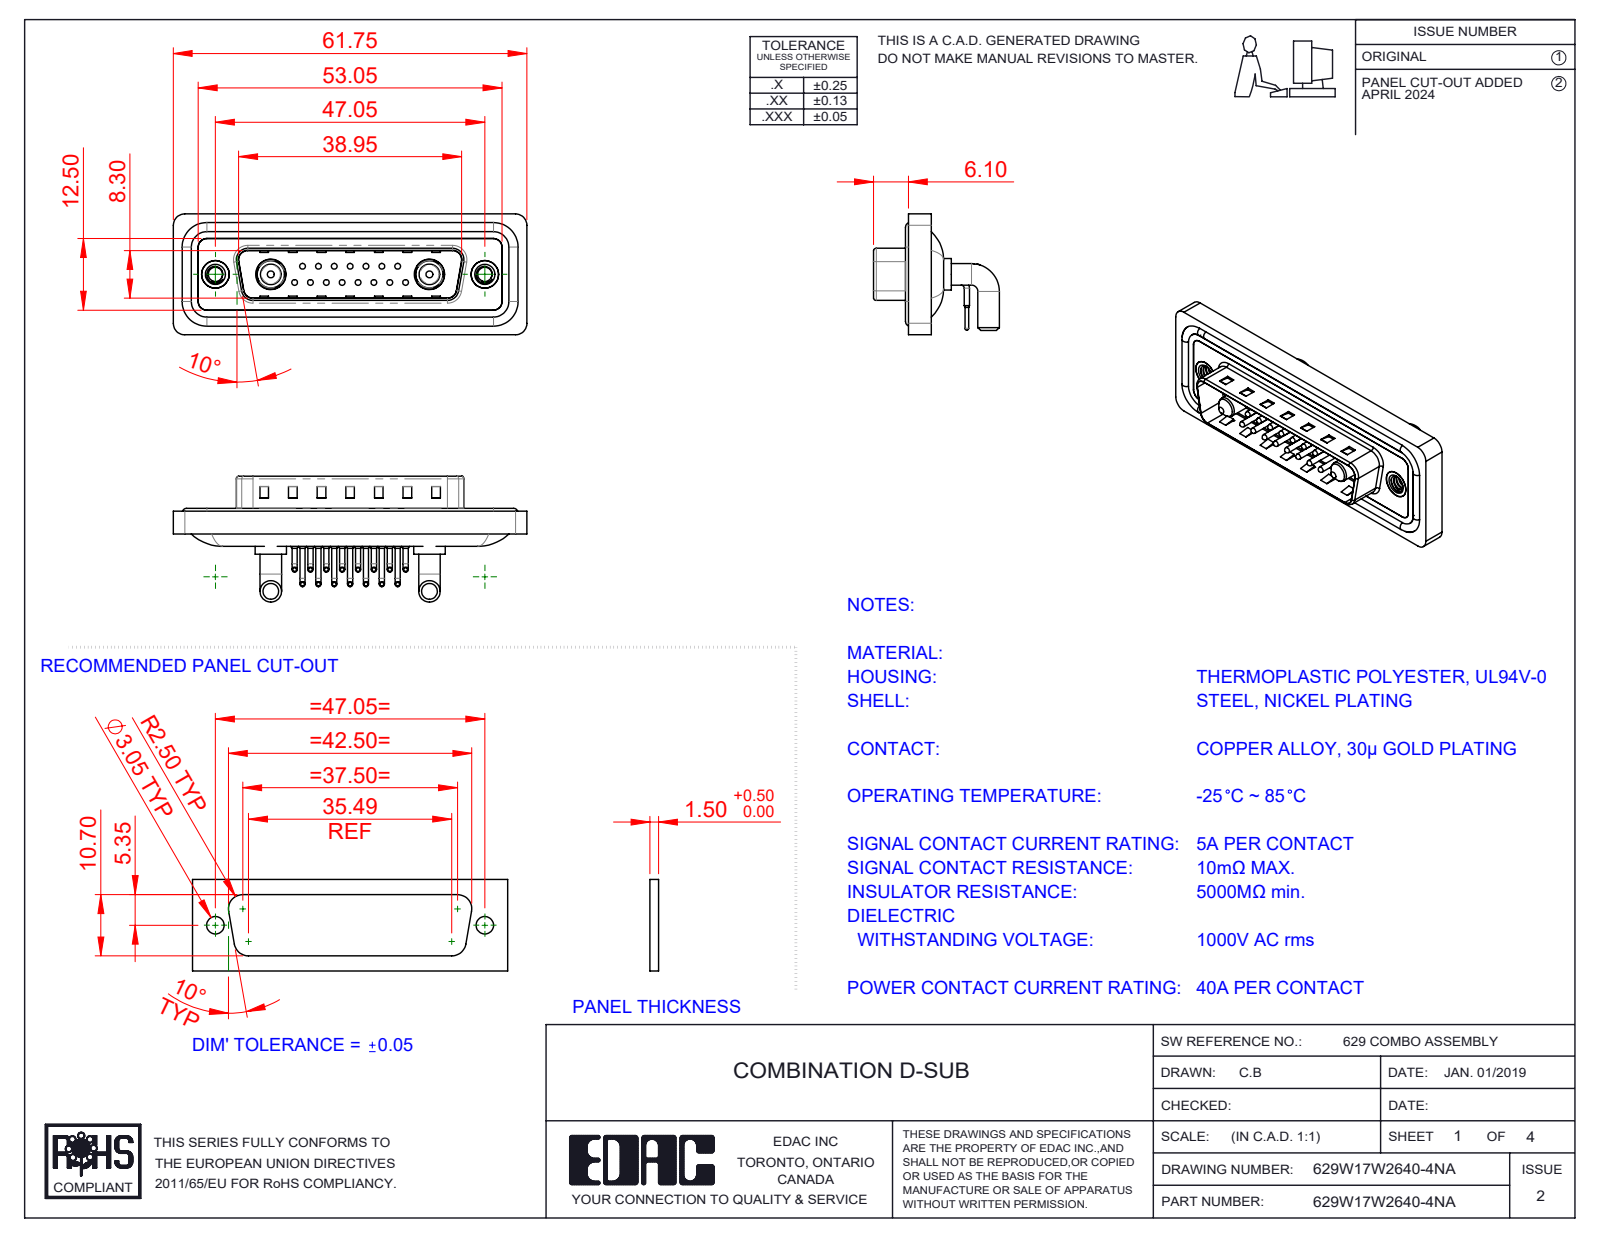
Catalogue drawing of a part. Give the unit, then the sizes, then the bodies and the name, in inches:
Units: inches
Overall size (bounding box): 2.431 × 0.865 × 0.831
Round holes (diameter × count): ⌀0.03 ×15, ⌀0.063 ×15, ⌀0.079 ×15, ⌀0.098 ×2, ⌀0.157 ×2, ⌀0.189 ×2, ⌀0.191 ×2, ⌀0.197 ×2, ⌀0.209 ×2
Round bosses / shafts (diameter × count): ⌀0.035 ×30, ⌀0.059 ×15, ⌀0.039 ×15, ⌀0.026 ×15, ⌀0.148 ×4, ⌀0.063 ×4, ⌀0.217 ×2, ⌀0.205 ×2
Partial cylindrical surfaces — rounded edges, fillets, slot ends (radius × count): R0.059 ×18, R0.079 ×18, R0.04 ×15, R0.02 ×8, R0.063 ×8, R0.01 ×4, R0.024 ×4, R0.026 ×4
Main face-to-face distances: 0.016, 0.114, 0.031, 0.161, 0.043, 0.083, 0.063, 0.177, 0.059, 0.098
Hole centre spacings: 0.124, 0.109, 0.218, 0.327, 0.198, 0.295, 0.436, 0.198
Volume: 0.468 in³ · Surface area: 19.67 in²
Bodies: 26 solids, 2213 faces (1189 planar, 768 cylindrical, 256 other)
Part name (STEP PRODUCT): 629Combo Shell Front_25 Contacts; 629Combo Contact Row 1; 629Combo Housing_17W2; 629Combo Contact Row 2 (+5 more)
STEP written by: SolidWorks 2023 (CONFIG_CONTROL_DESIGN)
